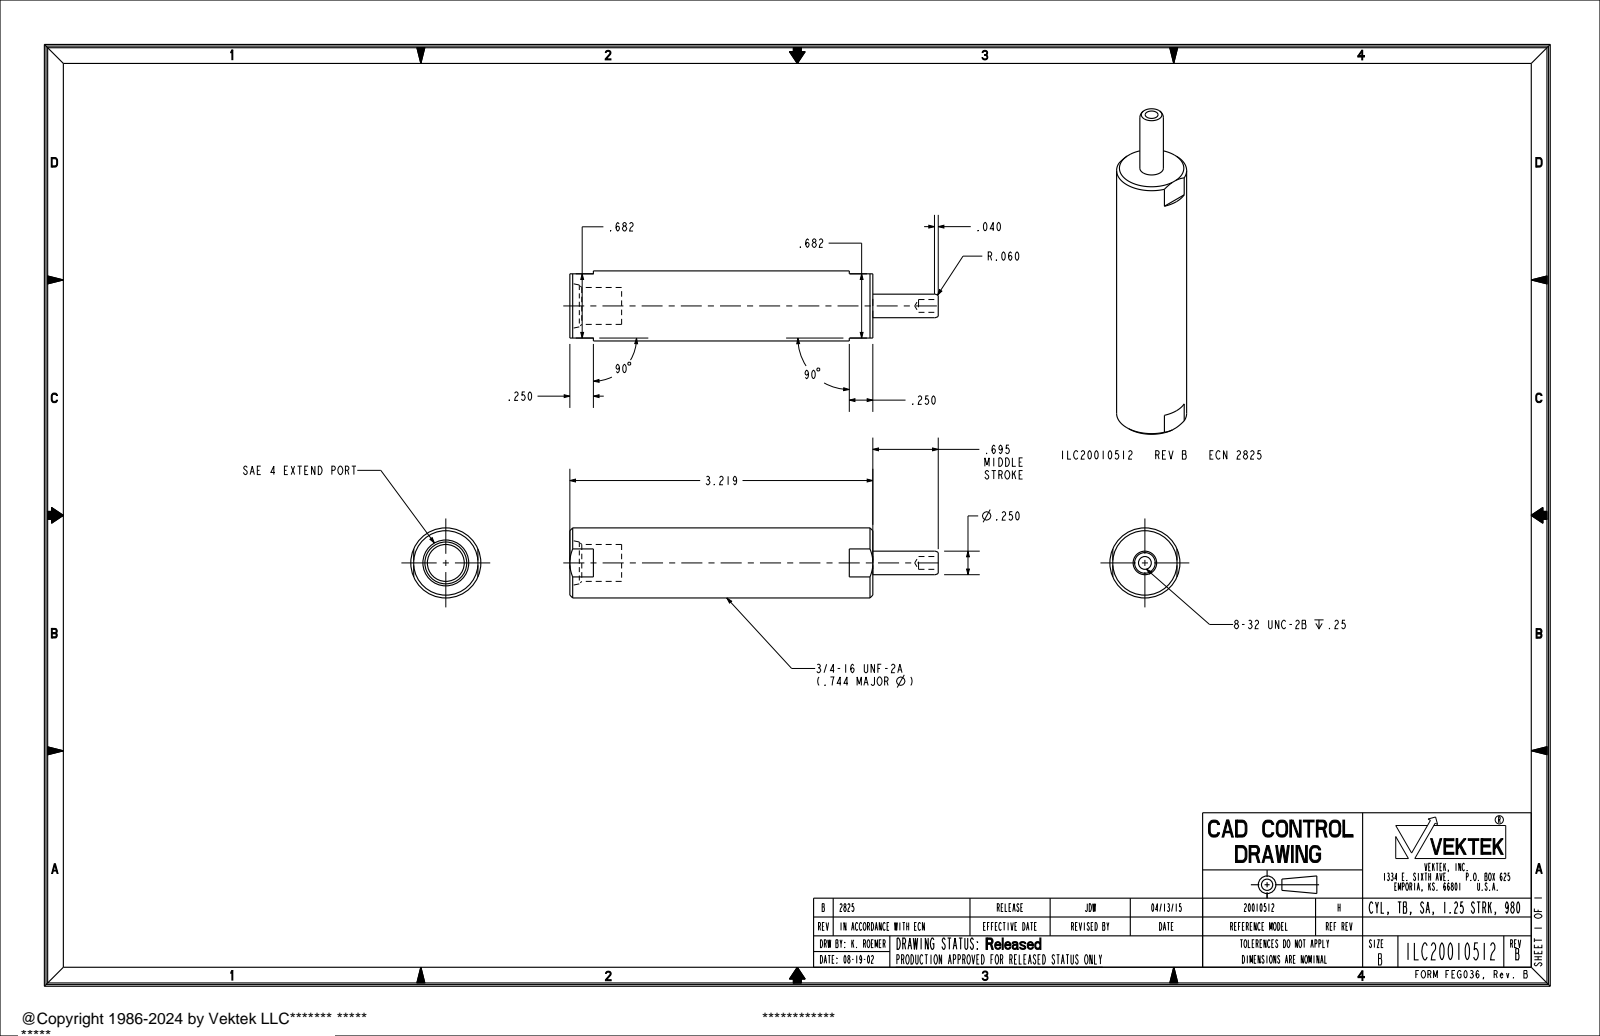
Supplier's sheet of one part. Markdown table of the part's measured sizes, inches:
| quantity | value |
| --- | --- |
| part name | ILC20010512 |
| STEP written by | PRO/ENGINEER BY PARAMETRIC TECHNOLOGY CORPORATION, 2013320 (AUTOMOTIVE_DESIGN) |
| units | inches |
| bodies | 1 solid, 32 faces (12 planar, 8 cylindrical, 12 other) |
| overall size | 3.914 × 0.744 × 0.744 |
| volume | 1.351 in³ |
| surface area | 9.598 in² |
| round holes (diameter × count) | 0.136 × 1, 0.392 × 1 |
| round bosses / shafts (diameter × count) | 0.744 × 1, 0.25 × 1 |
| main face-to-face distances | 3.219, 0.682, 0.55, 2.669, 0.25, 2.969, 3.914, 3.364, 0.695, 0.3 |
